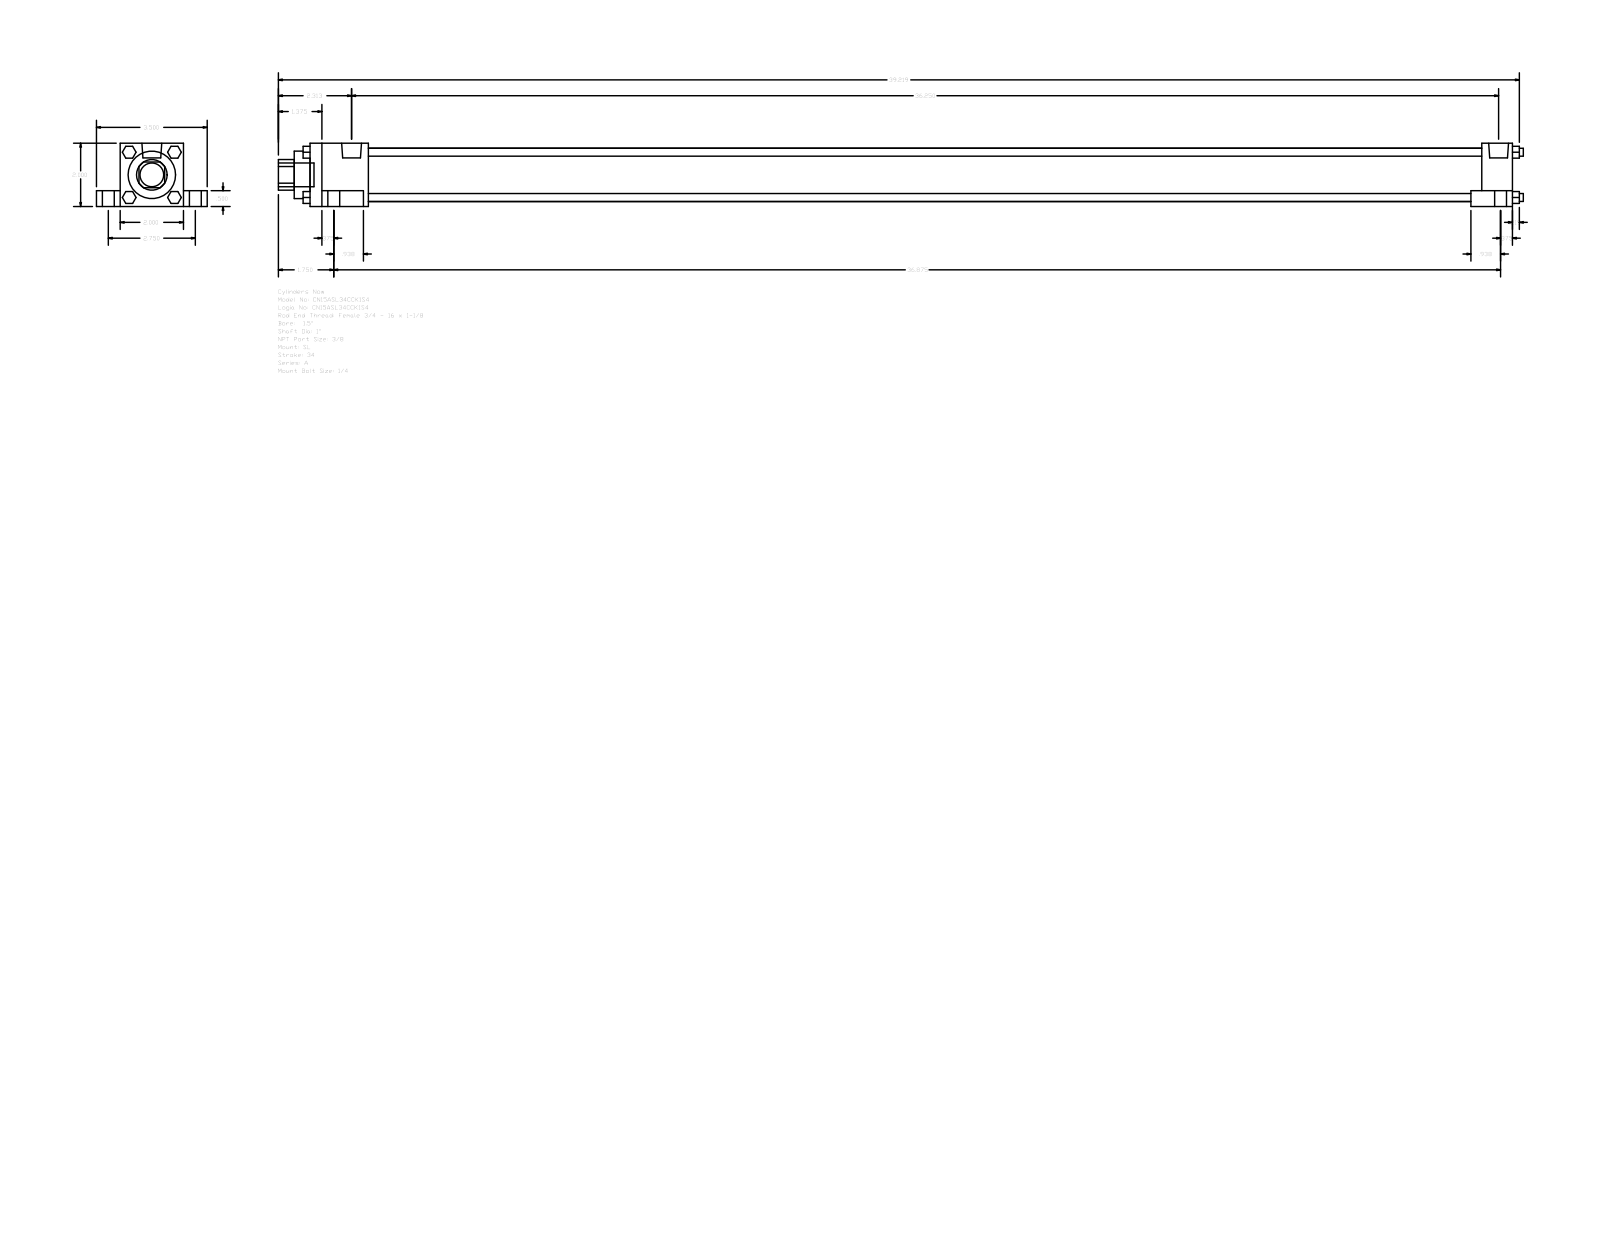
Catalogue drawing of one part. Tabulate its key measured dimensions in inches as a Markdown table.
| quantity | value |
| --- | --- |
| part name | A_SL__0150_1 |
| STEP written by | GSSL Pune (CONFIG_CONTROL_DESIGN) |
| units | inches |
| bodies | 0 solids, 148 faces (112 planar, 36 cylindrical, 0 other) |
| overall size | 39.344 × 3.5 × 2 |
| round holes (diameter × count) | 1 × 1, 1.5 × 1, 1.69 × 1 |
| round bosses / shafts (diameter × count) | 0.625 × 4, 0.375 × 4, 0.25 × 4, 0.219 × 4, 0.627 × 2, 0.75 × 1 |
| partial cylindrical surfaces (radius × count) | 0.484 × 1 |
| main face-to-face distances | 2, 0.5, 1.5, 0.75, 2.75, 0.375, 38, 1.313, 37.031, 0.969 |
